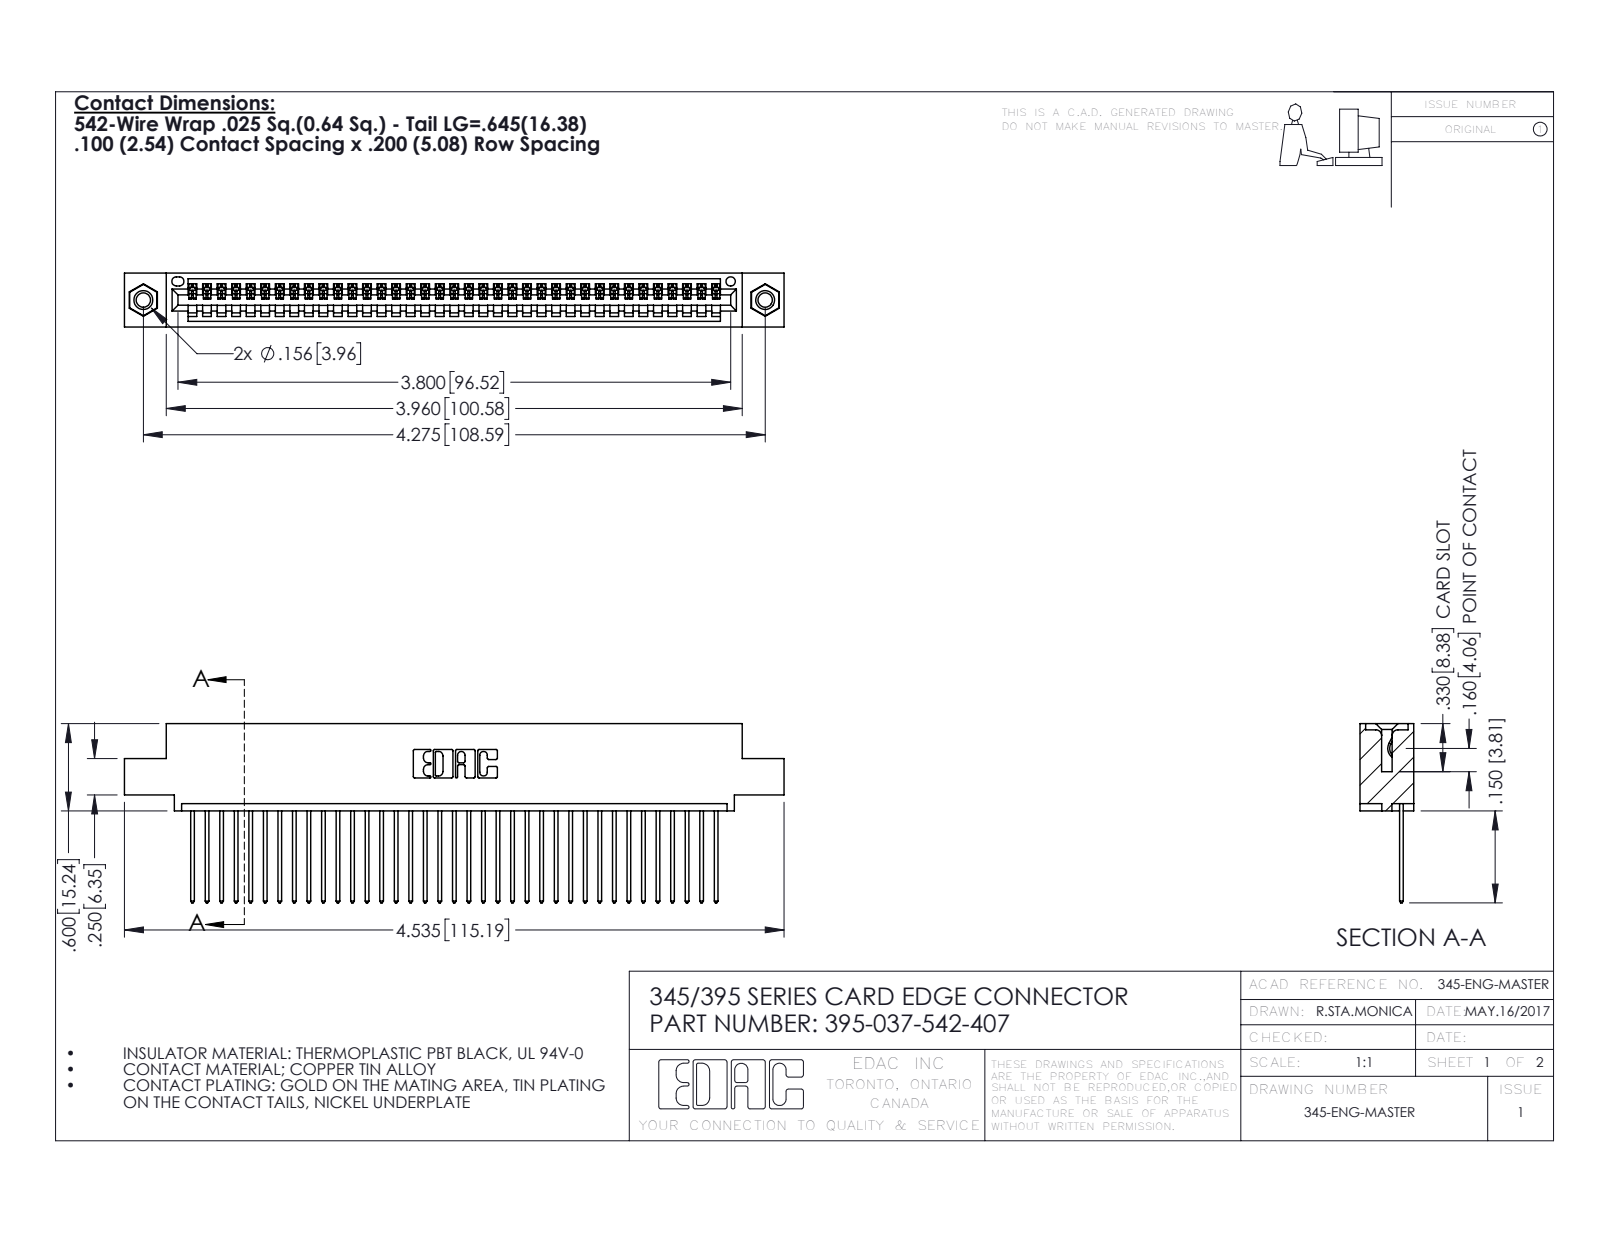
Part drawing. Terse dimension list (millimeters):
name: 345-292-001_345-293-142; 395-037-542-407; 345 Part_0.110 Offset - 0.156 Dia-TI; 345-250-001_345-250-005-103
written by: SolidWorks 2016 (CONFIG_CONTROL_DESIGN)
unit: mm
bodies: 40 solids, 2336 faces (1596 planar, 724 cylindrical, 16 other)
size: 115.2 × 31.3 × 9.4
volume: 10 900 mm³; area: 15 050 mm²
holes: 2× ⌀2.5, 2× ⌀3.2, 2× ⌀4, 1× ⌀1.6
bosses: 2× ⌀3.9
rounds: 74× R0.2, 74× R0.3, 22× R0.3, 6× R0.2, 6× R0.8, 3× R0.7, 2× R0.8, 2× R1
face distances: 1.8, 7.6, 9.4, 2.5, 6.9, 0.6, 5.1, 5.7, 3.8, 1.8
hole spacings: 6.9, 102.6, 108.6
